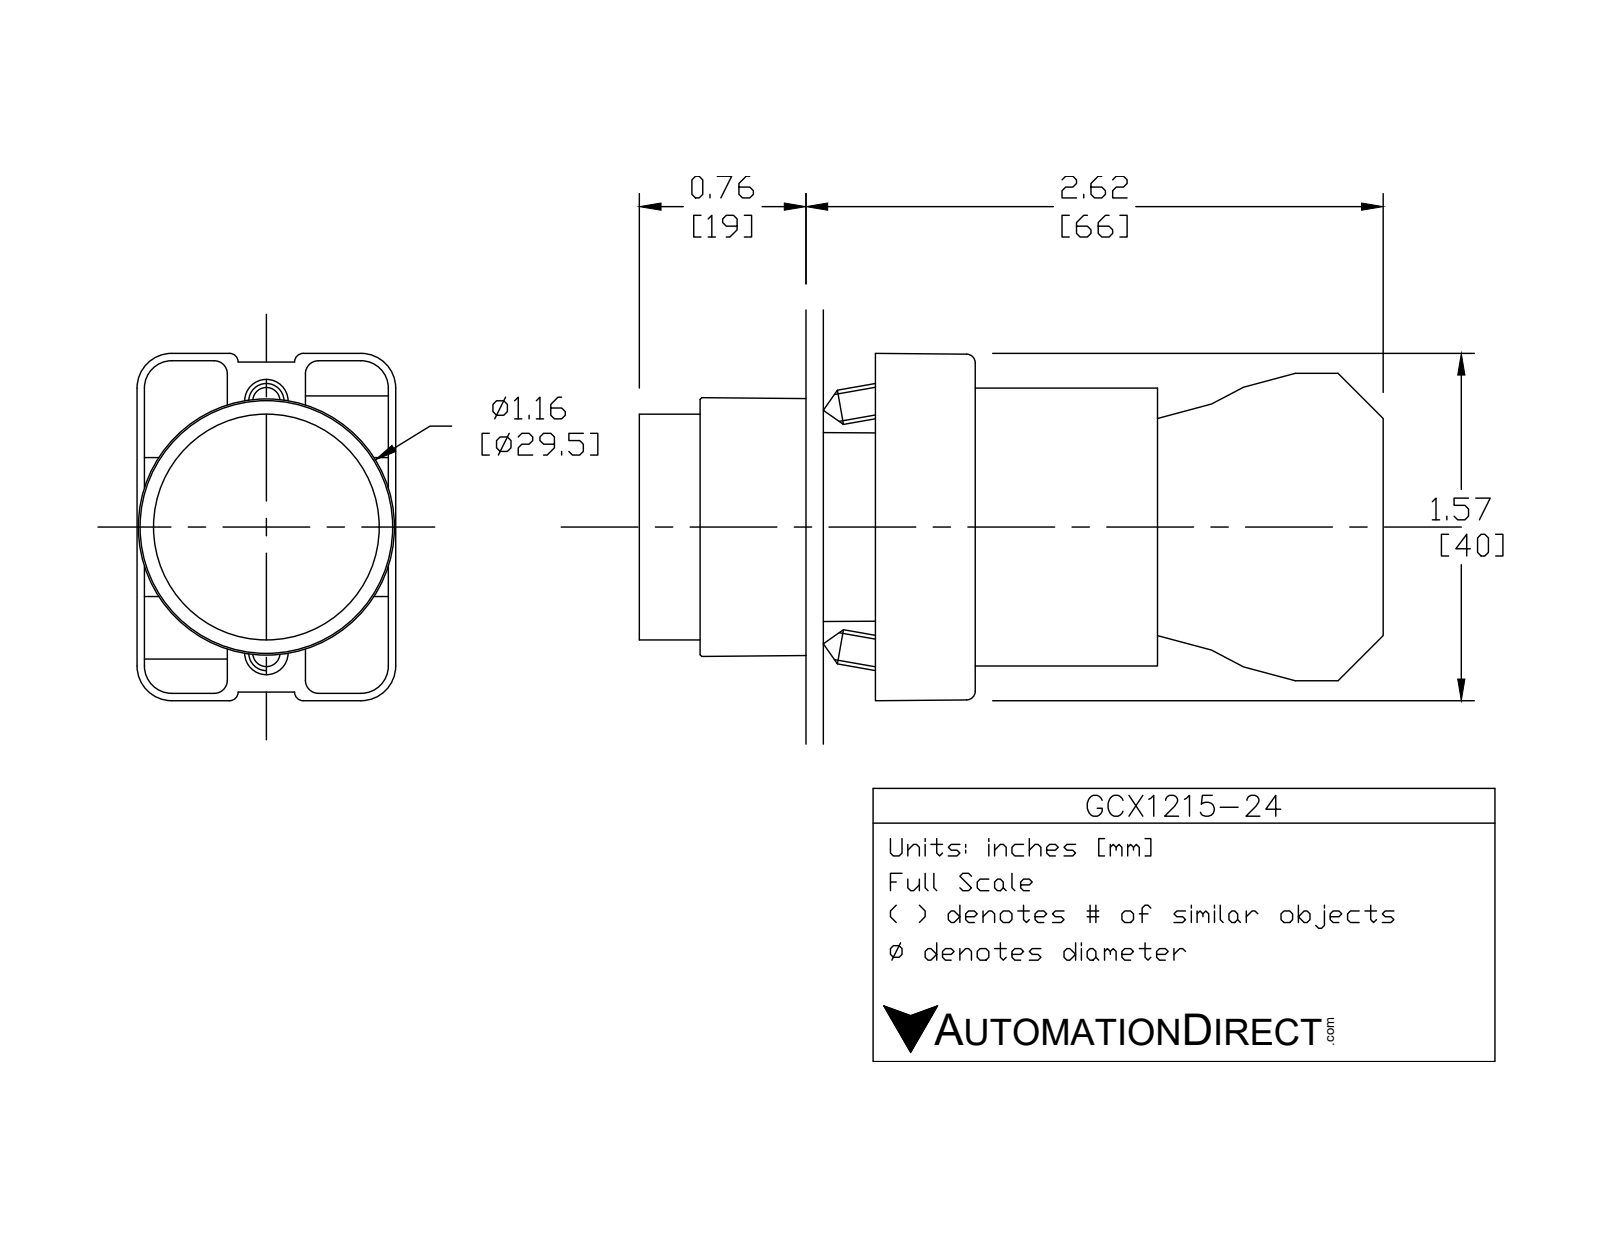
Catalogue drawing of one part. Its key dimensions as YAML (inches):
part_name: "ecx1029; GCX1215-24; ecx1040; GCX1215 OPERATOR (+1 more)"
step_written_by: "SolidWorks 2016 (AUTOMOTIVE_DESIGN)"
units: inches
bodies: {solids: 7, faces: 425, planar: 250, cylindrical: 144, other: 31}
overall_size: [3.319, 1.581, 1.177]
volume: 2.721
surface_area: 36.32
round_holes:
  - {diameter: 0.079, count: 2}
  - {diameter: 0.124, count: 2}
  - {diameter: 0.13, count: 2}
  - {diameter: 0.087, count: 1}
  - {diameter: 0.197, count: 1}
  - {diameter: 0.469, count: 1}
  - {diameter: 0.878, count: 1}
  - {diameter: 0.888, count: 1}
  - {diameter: 1.024, count: 1}
round_bosses_or_shafts:
  - {diameter: 0.157, count: 4}
  - {diameter: 1.175, count: 1}
  - {diameter: 1.004, count: 1}
  - {diameter: 0.945, count: 1}
  - {diameter: 0.856, count: 1}
  - {diameter: 0.78, count: 1}
  - {diameter: 0.504, count: 1}
partial_cylinders:
  - {radius: 0.059, count: 24}
  - {radius: 0.041, count: 12}
  - {radius: 0.124, count: 12}
  - {radius: 0.157, count: 12}
  - {radius: 0.039, count: 8}
  - {radius: 0.128, count: 2}
  - {radius: 0.02, count: 1}
  - {radius: 0.063, count: 1}
face_to_face_distances: [0.827, 0.579, 1.171, 2.02, 1.193, 0.031, 0.033, 0.573, 1.165, 0.593]
hole_center_spacings: [0.236, 0.544, 0.472, 0.49]
